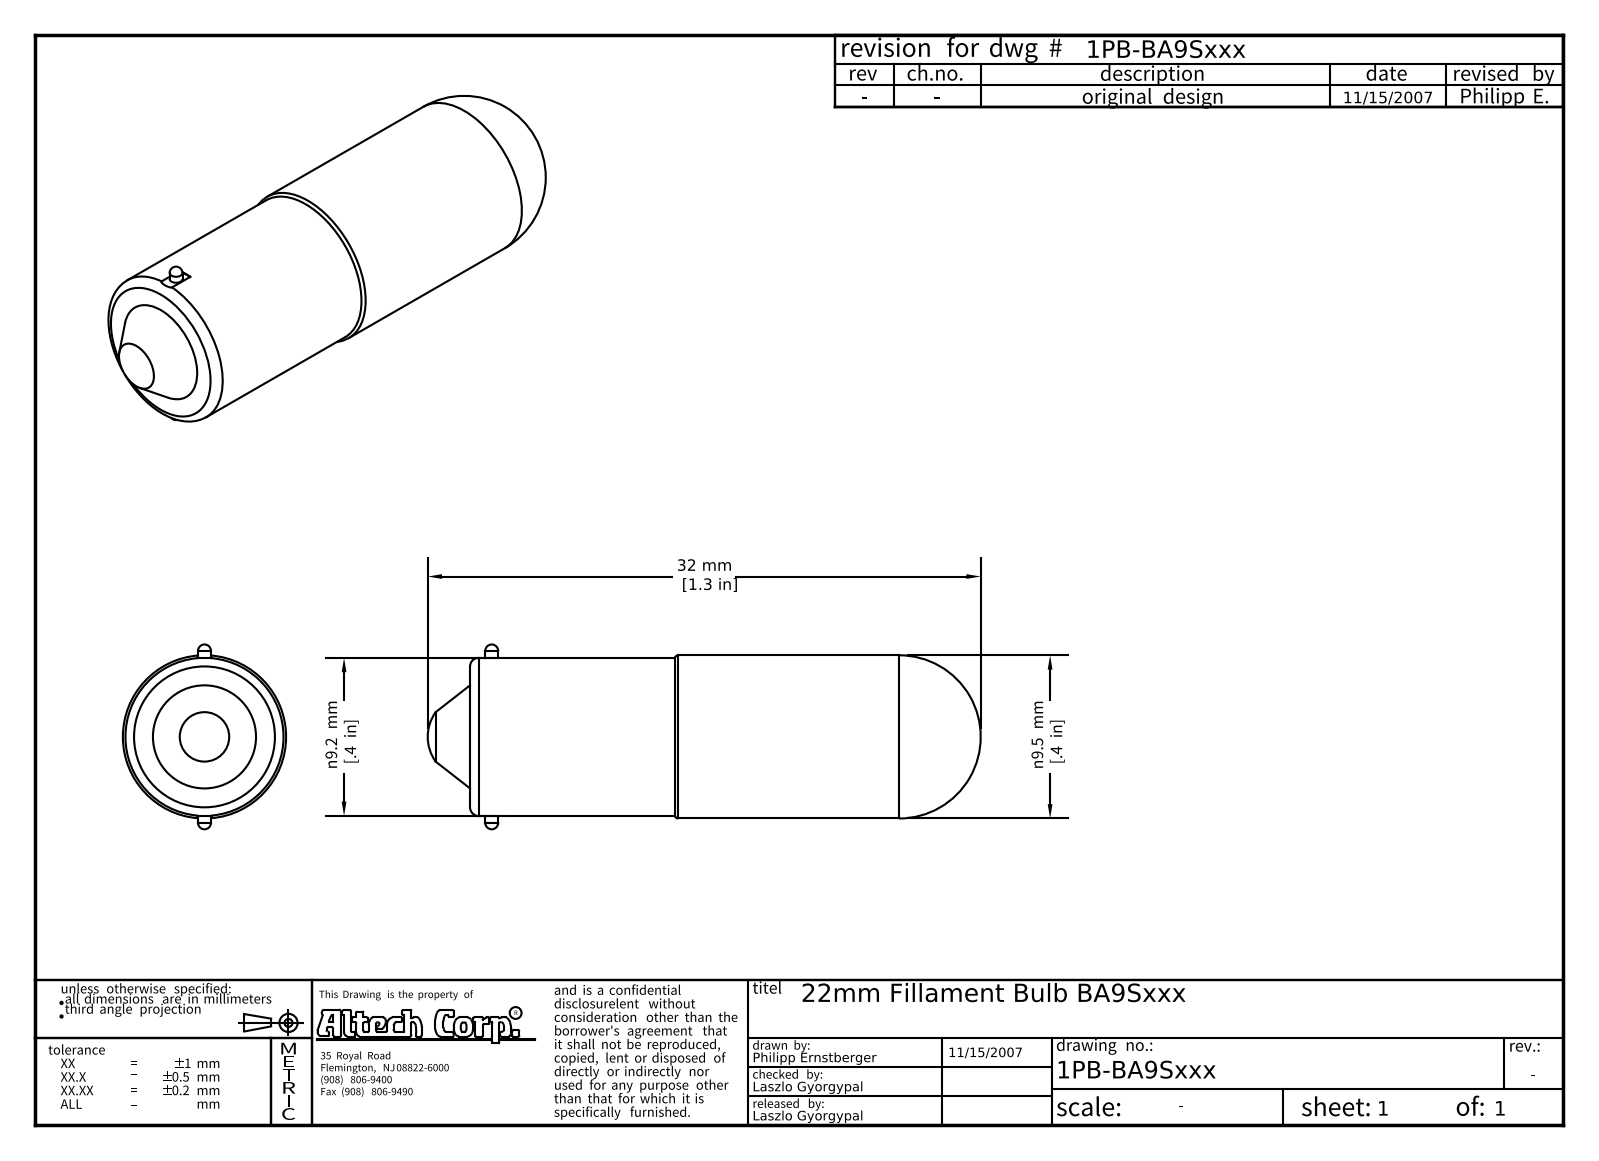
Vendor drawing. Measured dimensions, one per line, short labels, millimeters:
name: BA9Sxxx
written by: Autodesk Inventor 2008 (AUTOMOTIVE_DESIGN)
unit: mm
bodies: 1 solid, 16 faces (5 planar, 3 cylindrical, 8 other)
size: 32.19 × 10.76 × 9.5
volume: 1 975 mm³; area: 955 mm²
bosses: 1× ⌀9.5, 1× ⌀9.2, 1× ⌀0.75
face distances: 9.16, 2
